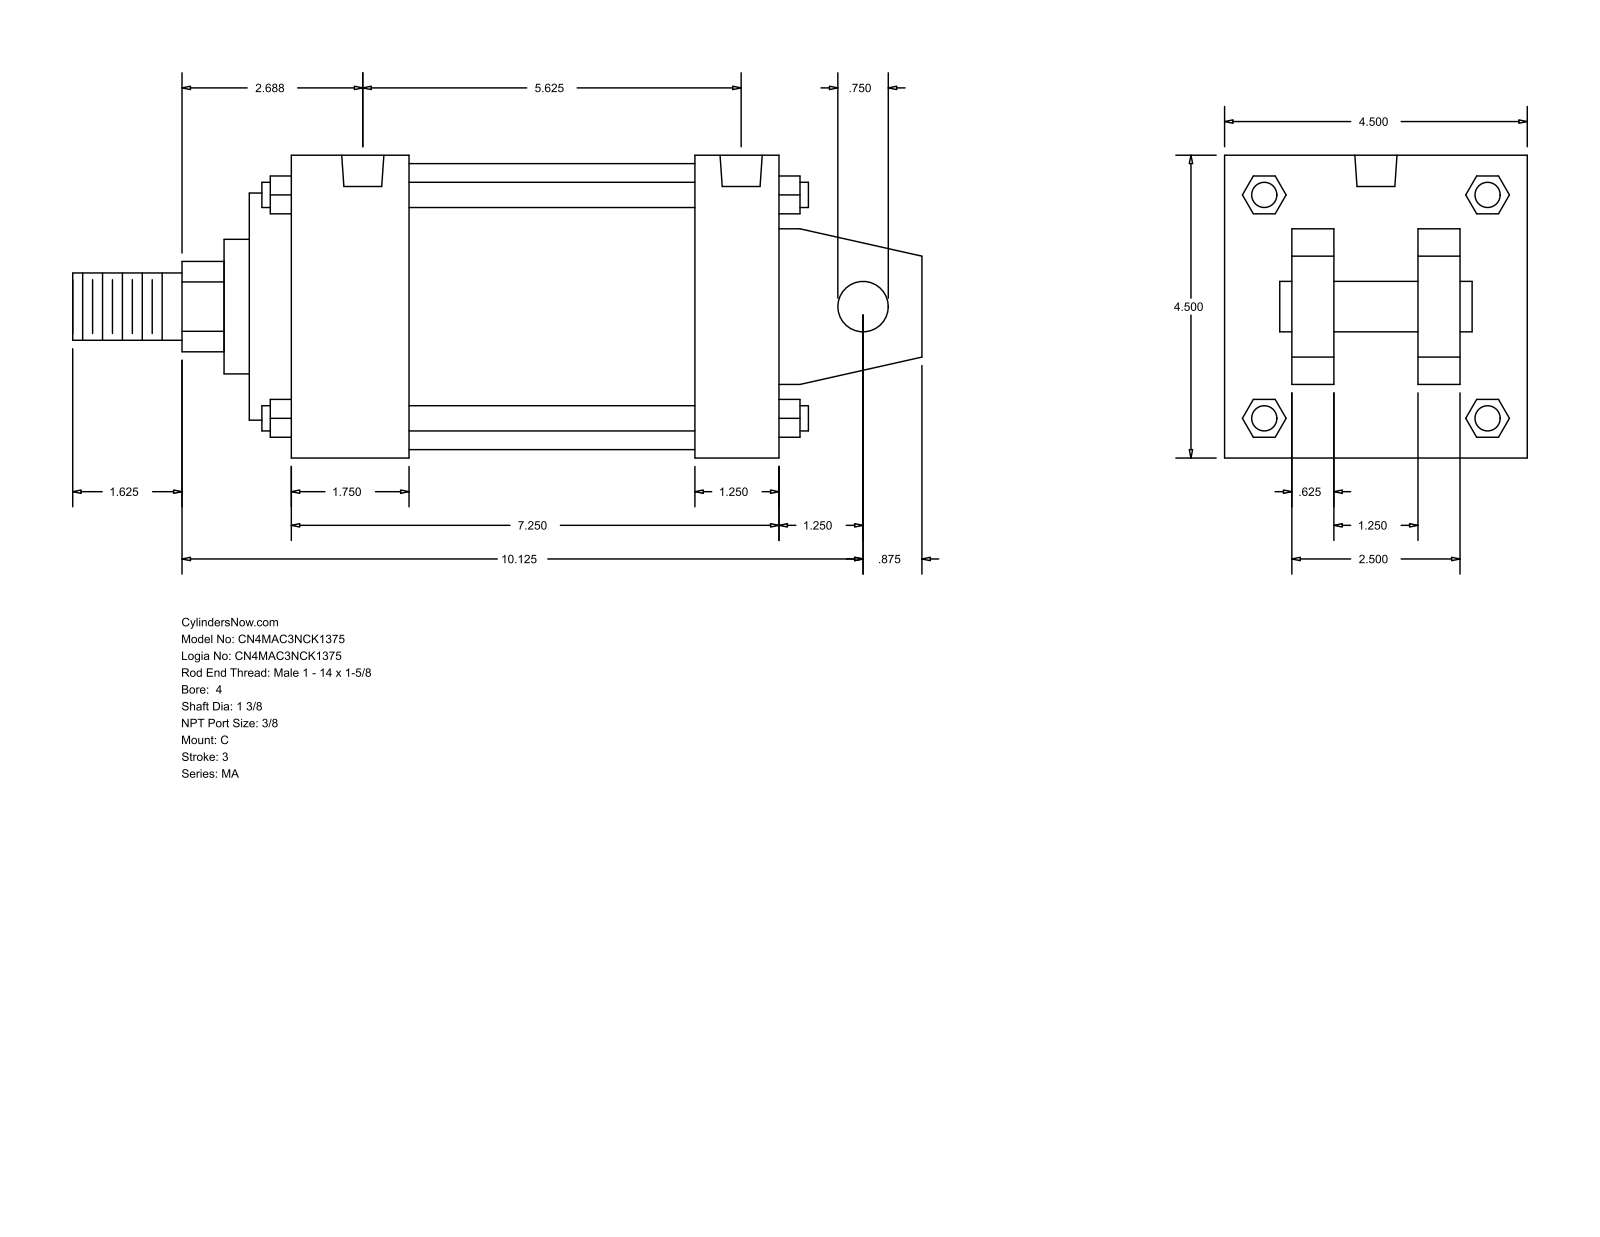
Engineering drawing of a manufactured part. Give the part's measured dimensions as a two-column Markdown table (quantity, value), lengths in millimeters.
| quantity | value |
| --- | --- |
| part name | MA_C__0400_1.375 |
| STEP written by | GSSL Pune (CONFIG_CONTROL_DESIGN) |
| units | millimeters |
| bodies | 0 solids, 141 faces (109 planar, 32 cylindrical, 0 other) |
| overall size | 320.68 × 114.3 × 114.3 |
| round holes (diameter × count) | 11.11 × 4, 15.93 × 2 |
| round bosses / shafts (diameter × count) | 9.53 × 4, 107.95 × 1, 85.72 × 1, 50.8 × 1, 34.92 × 1, 25.4 × 1, 19.05 × 1 |
| partial cylindrical surfaces (radius × count) | 17.06 × 1 |
| main face-to-face distances | 114.3, 15.87, 184.16, 73.03, 41.27, 25.4, 88.9, 47.63, 200.03, 168.28 |
| hole center spacings | 133.35, 4.76, 4.77, 138.11, 138.12, 142.88 |
